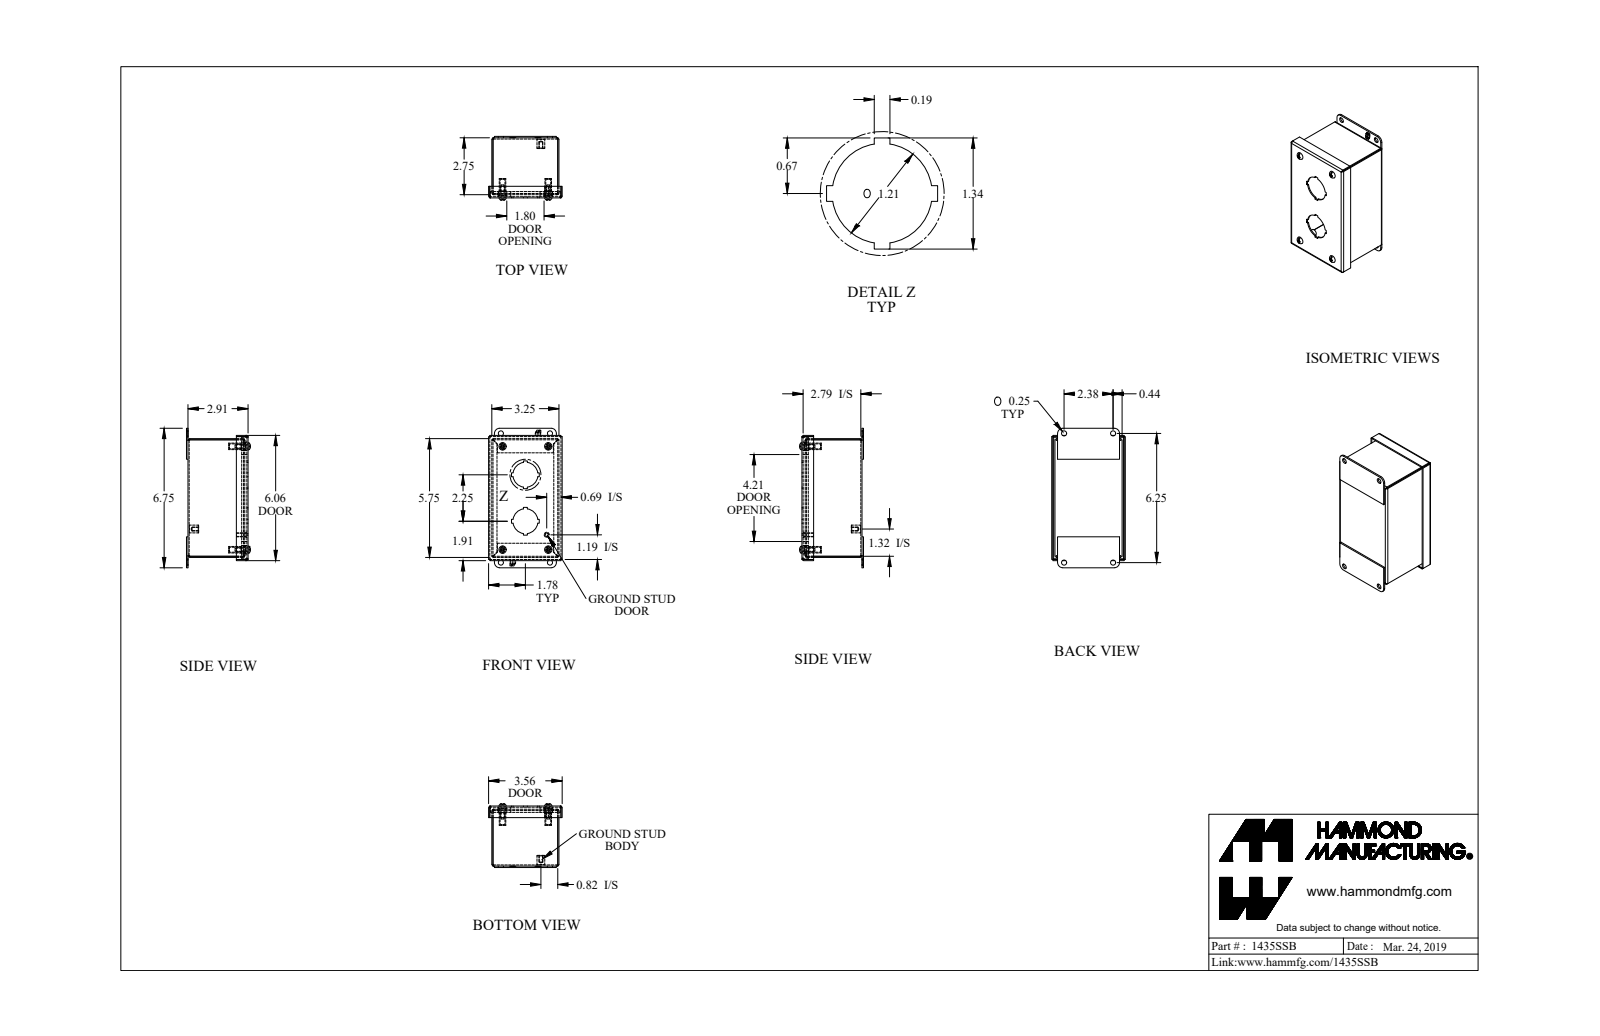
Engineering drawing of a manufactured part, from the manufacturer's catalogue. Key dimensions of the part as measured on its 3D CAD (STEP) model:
Part name (STEP PRODUCT): 1435SSB_Default
STEP written by: SolidWorks 2019 (CONFIG_CONTROL_DESIGN)
Units: inches
Bodies: 19 solids, 477 faces (307 planar, 140 cylindrical, 30 other)
Overall size (bounding box): 6.75 × 3.562 × 3.089
Volume: 8.251 in³ · Surface area: 255.2 in²
Round holes (diameter × count): ⌀0.25 ×8, ⌀0.065 ×4, ⌀0.239 ×4, ⌀0.253 ×4, ⌀0.406 ×4, ⌀1.21 ×2, ⌀0.156 ×1
Round bosses / shafts (diameter × count): ⌀0.19 ×5, ⌀0.406 ×4, ⌀0.315 ×4, ⌀0.148 ×4, ⌀0.375 ×1, ⌀0.25 ×1
Partial cylindrical surfaces — rounded edges, fillets, slot ends (radius × count): R0.029 ×12, R0.086 ×12, R0.171 ×4, R0.25 ×4
Main face-to-face distances: 0.057, 2.85, 0.057, 3.193, 2.907, 2.793, 5.693, 3.136, 3.25, 0.156
Hole centre spacings: 5, 0.63, 0.631, 2.211, 2.376, 2.377, 5.467, 5.626
